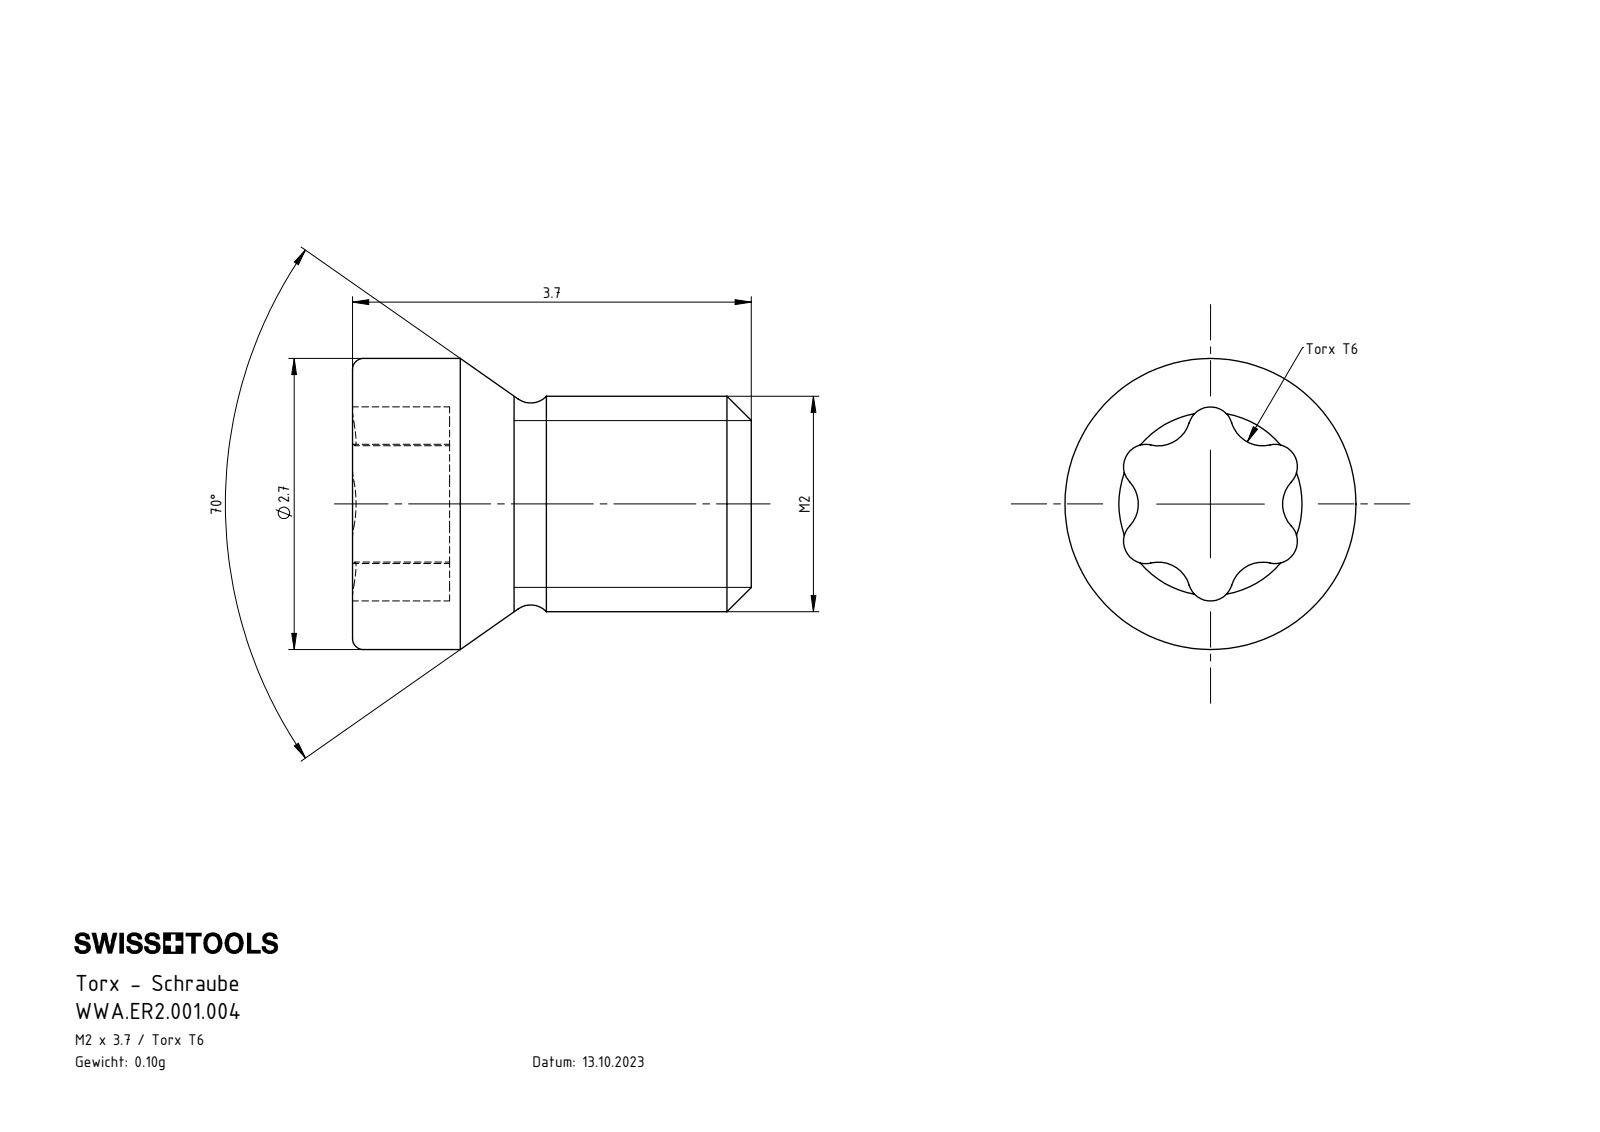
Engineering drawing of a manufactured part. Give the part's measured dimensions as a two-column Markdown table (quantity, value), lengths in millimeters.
| quantity | value |
| --- | --- |
| part name | WWA.ER2.001.004 |
| STEP written by | SolidWorks 2017 (AUTOMOTIVE_DESIGN) |
| units | millimeters |
| bodies | 1 solid, 41 faces (3 planar, 19 cylindrical, 19 other) |
| overall size | 3.7 × 2.7 × 2.7 |
| volume | 13 mm³ |
| surface area | 40 mm² |
| round bosses / shafts (diameter × count) | 2.7 × 1, 2 × 1 |
| partial cylindrical surfaces (radius × count) | 0.21 × 6, 0.3 × 6 |
| main face-to-face distances | 0.9, 3.7, 2.8 |
